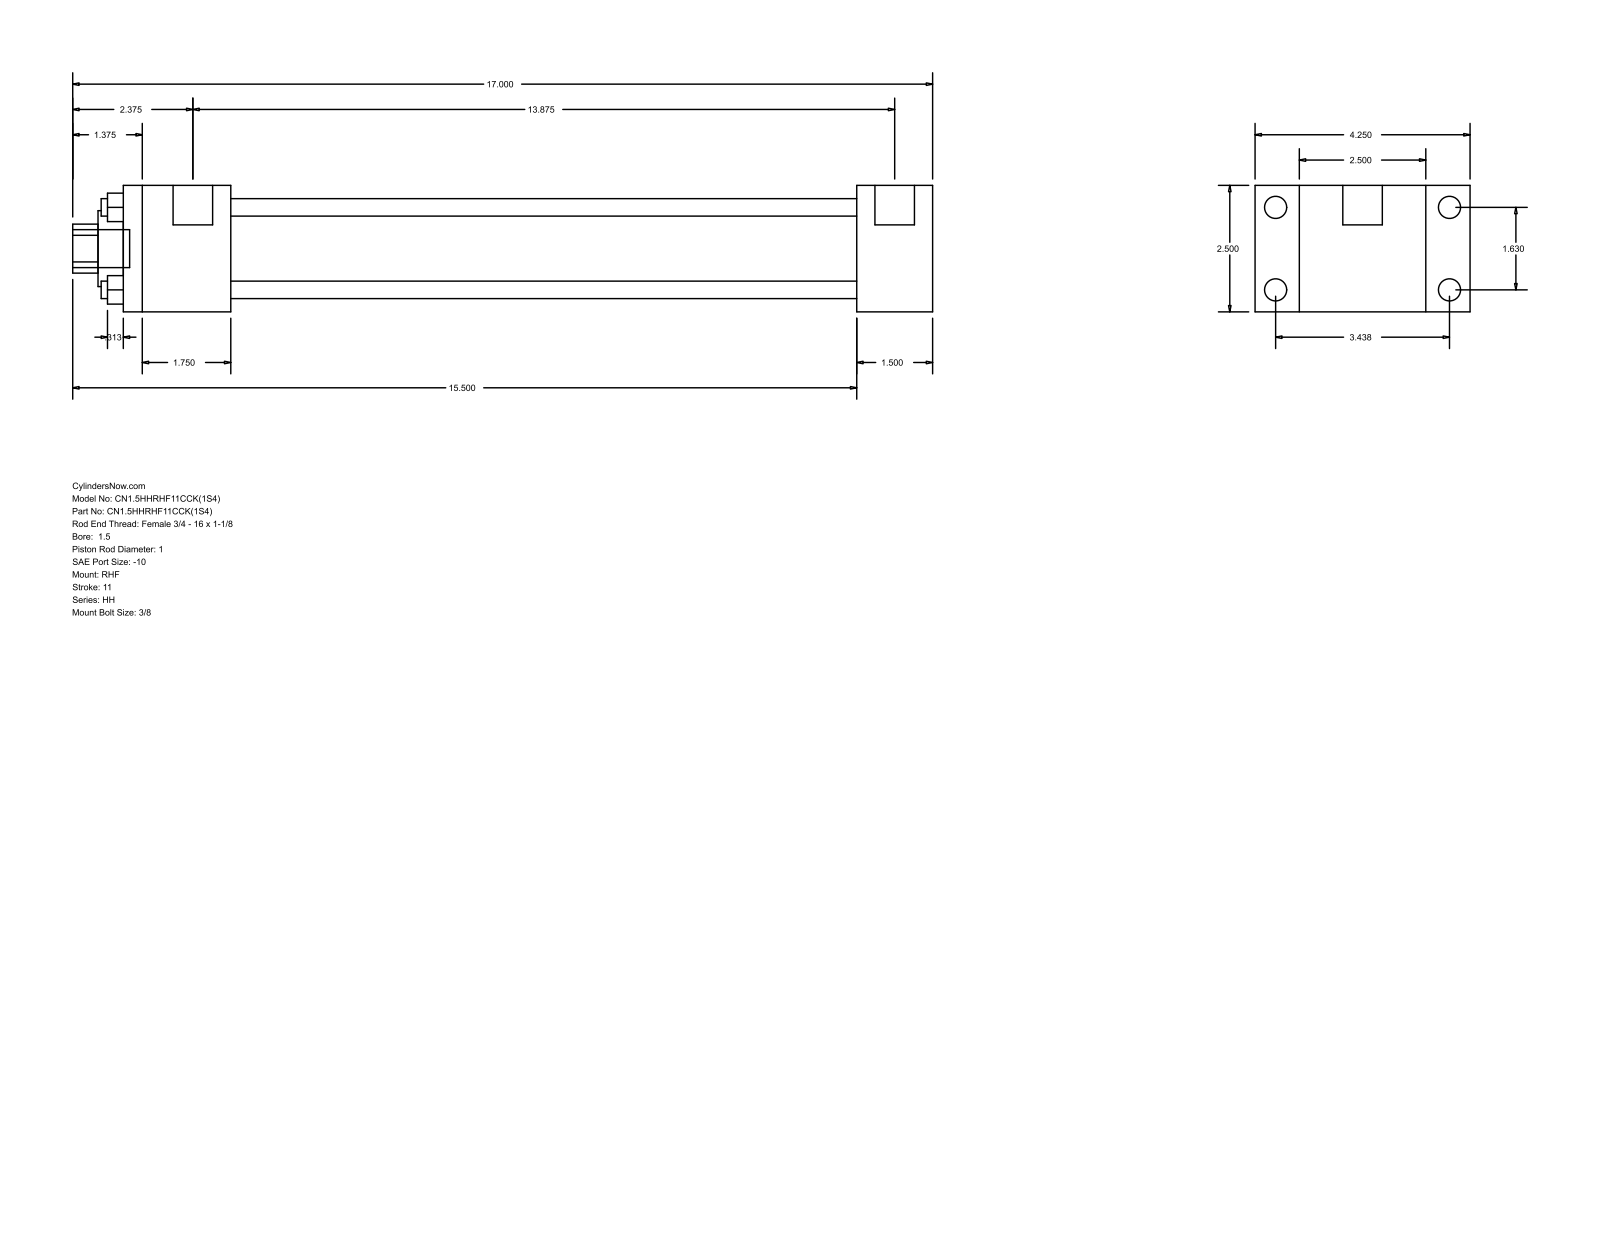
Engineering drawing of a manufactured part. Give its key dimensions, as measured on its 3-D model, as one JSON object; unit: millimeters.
{"part_name": "HH_RHF__0150_1", "step_written_by": "GSSL Pune (CONFIG_CONTROL_DESIGN)", "units": "millimeters", "bodies": {"solids": 0, "faces": 88, "planar": 60, "cylindrical": 28, "other": 0}, "overall_size": [431.8, 107.95, 63.5], "round_holes": [[8.76, 4], [25.4, 1], [38.1, 1], [44.45, 1]], "round_bosses_or_shafts": [[11.13, 4], [5.56, 4], [19.84, 2], [19.05, 1]], "partial_cylinders_radius": [[12.29, 1]], "face_to_face_distances": [63.5, 22.23, 85.73, 38.1, 107.96, 314.32, 352.42, 53.98, 368.3, 406.4], "hole_center_spacings": [29.27, 41.4, 58.55]}
